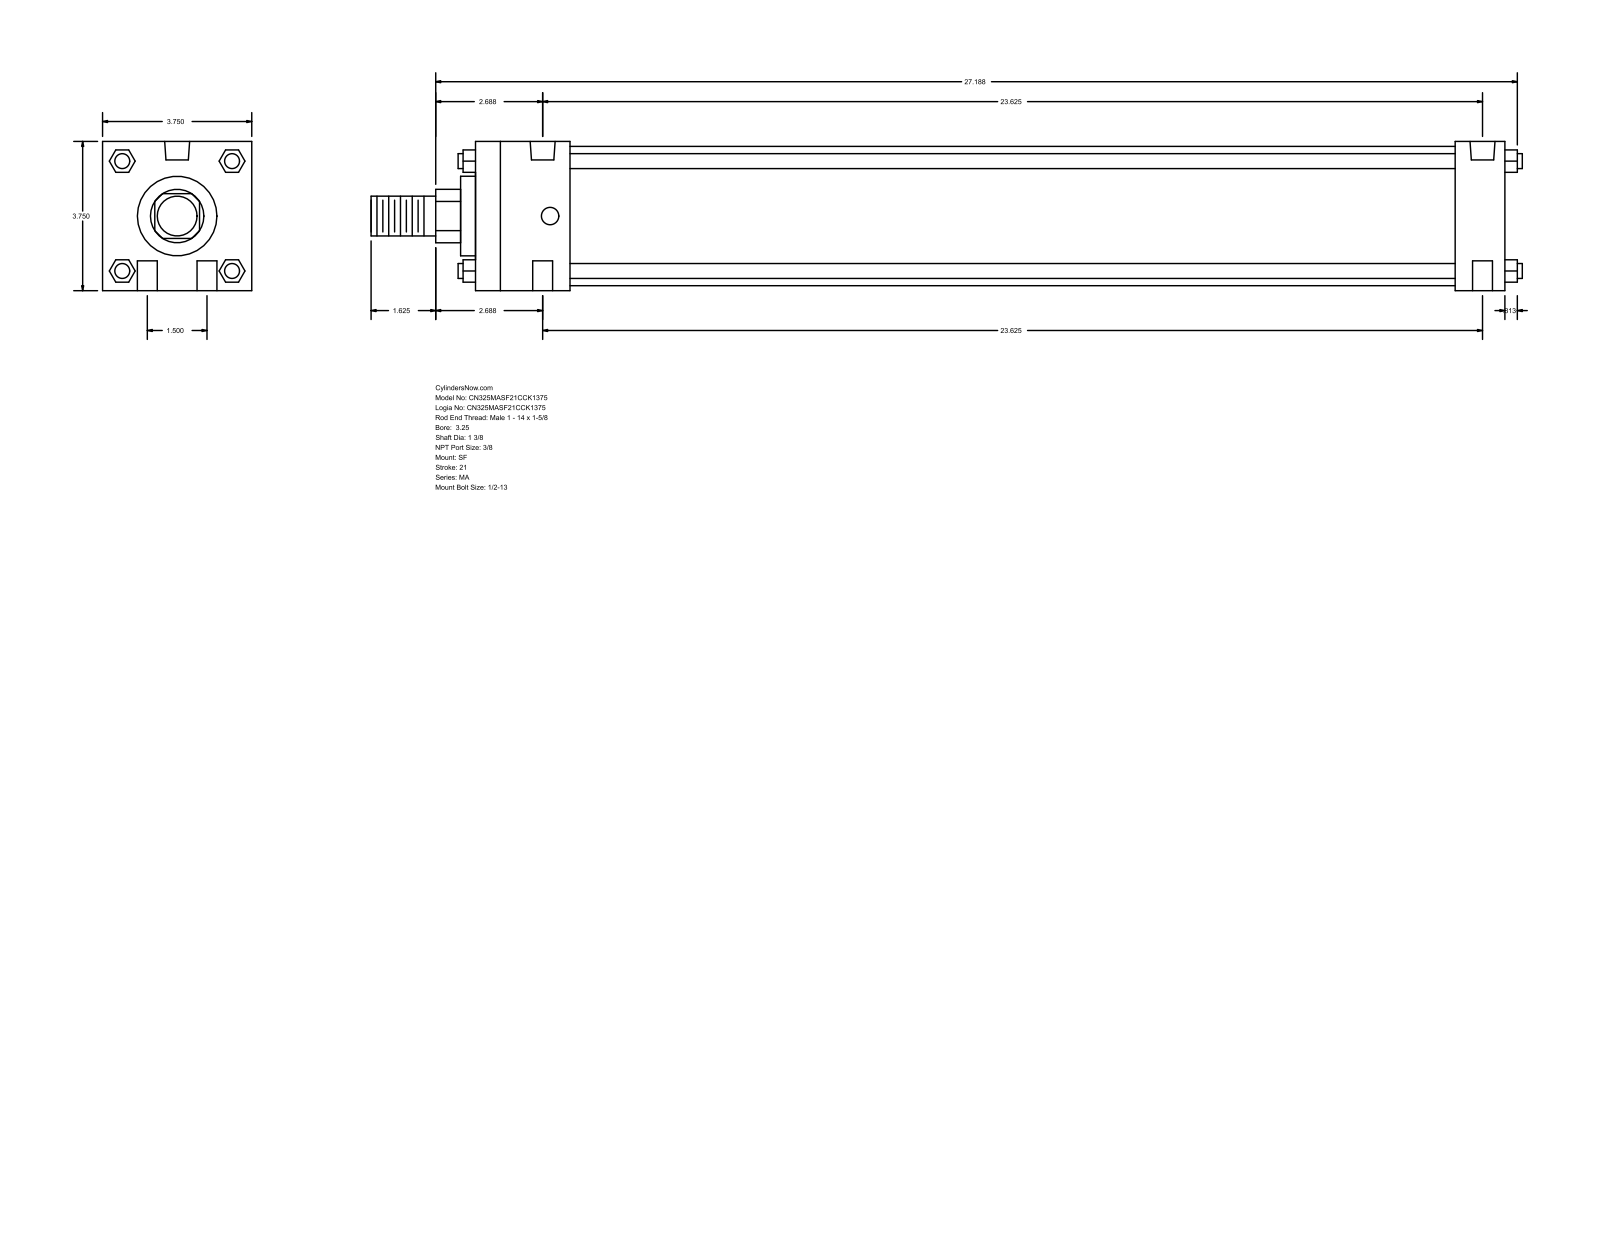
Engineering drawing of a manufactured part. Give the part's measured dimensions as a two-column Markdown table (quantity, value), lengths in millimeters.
| quantity | value |
| --- | --- |
| part name | MA_SF__0325_1.375 |
| STEP written by | GSSL Pune (CONFIG_CONTROL_DESIGN) |
| units | millimeters |
| bodies | 0 solids, 124 faces (94 planar, 30 cylindrical, 0 other) |
| overall size | 735.01 × 95.25 × 95.25 |
| round holes (diameter × count) | 12.7 × 4, 11.11 × 2, 15.93 × 2 |
| round bosses / shafts (diameter × count) | 9.53 × 4, 88.9 × 1, 50.8 × 1, 34.92 × 1, 25.4 × 1 |
| partial cylindrical surfaces (radius × count) | 17.06 × 1 |
| main face-to-face distances | 95.24, 657.22, 625.48, 31.74, 60.32, 565.16, 596.9, 9.52, 69.84, 635 |
| hole center spacings | 19.05, 600.38, 600.08, 38.1, 601.29, 590.55 |
